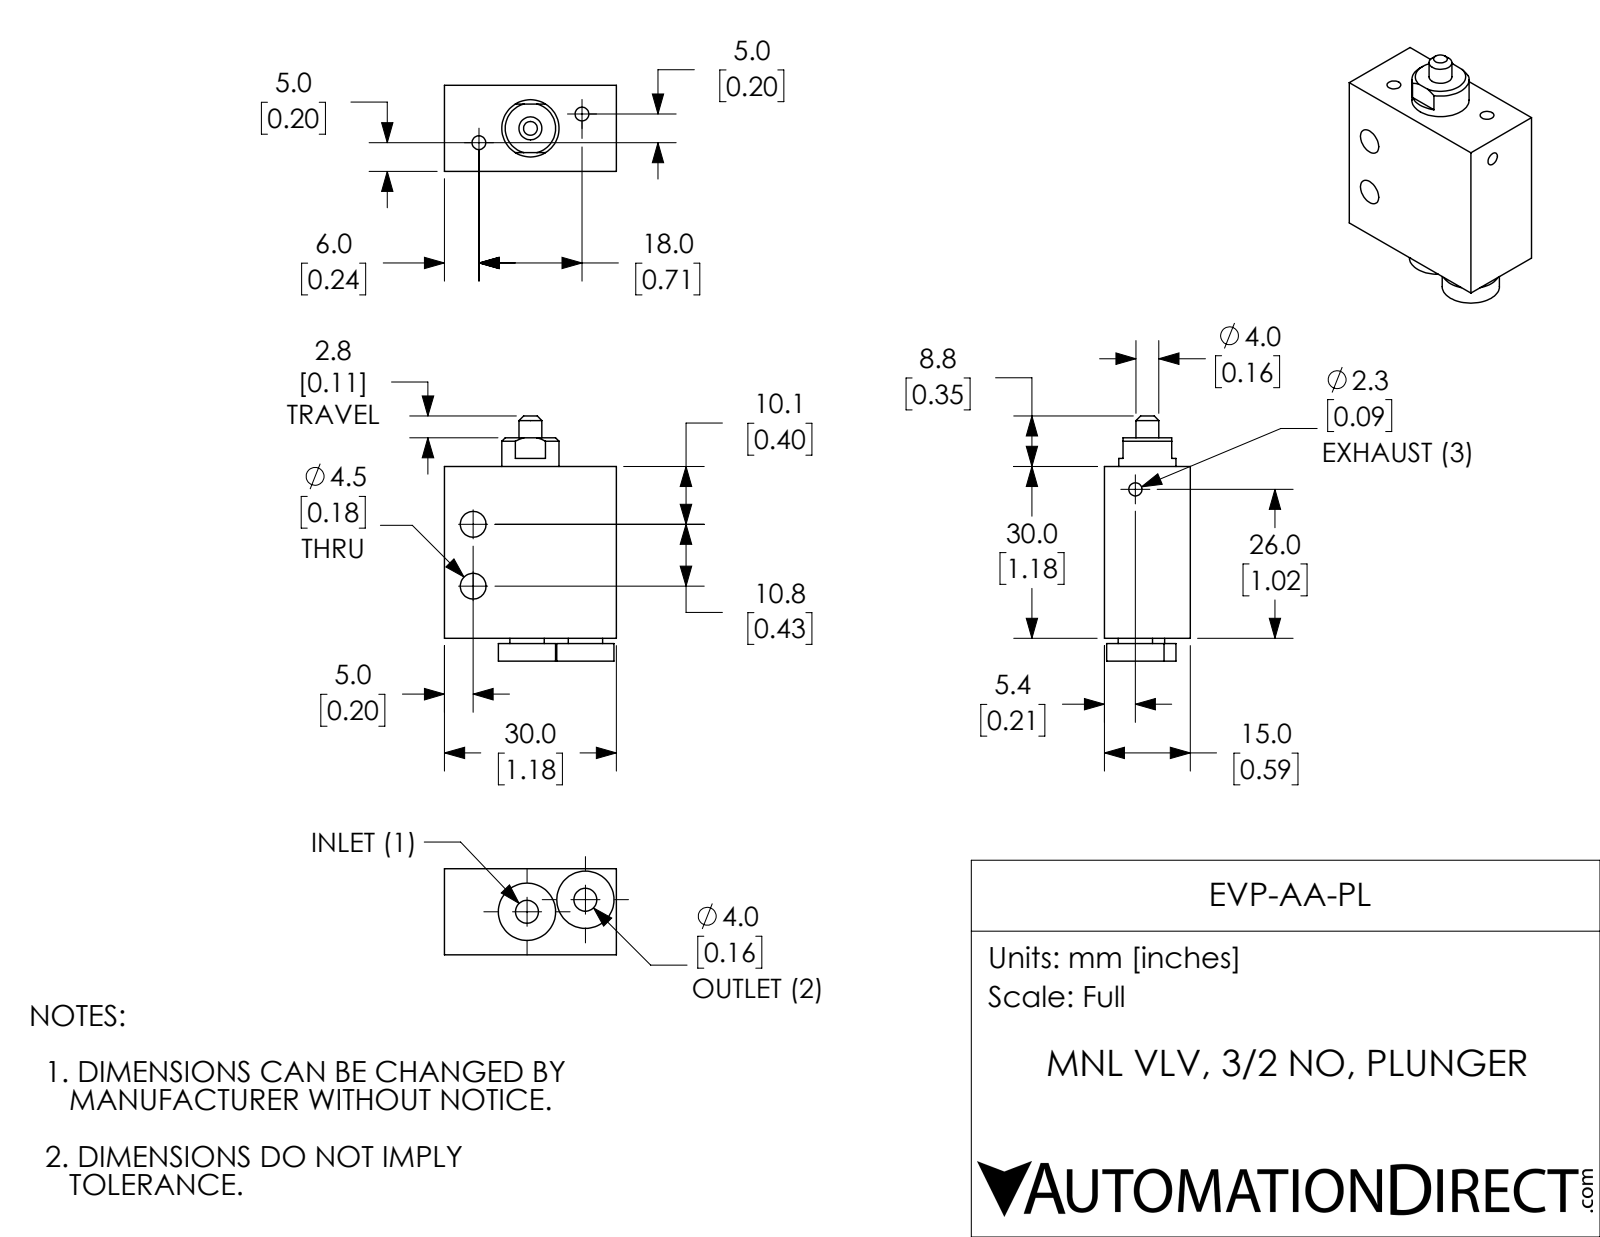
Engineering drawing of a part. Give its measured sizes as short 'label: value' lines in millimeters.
name: EVP-AA-PL
written by: SolidWorks 2017 (AUTOMOTIVE_DESIGN)
unit: mm
bodies: 1 solid, 51 faces (21 planar, 26 cylindrical, 4 other)
size: 42.8 × 30 × 15
volume: 13 800 mm³; area: 4 811 mm²
holes: 2× ⌀2.4, 2× ⌀4, 2× ⌀4.5, 1× ⌀2.3
bosses: 3× ⌀10, 2× ⌀6, 1× ⌀4
face distances: 15, 30, 4, 34, 3.1, 0.9, 30.9, 39, 35.9, 35
hole spacings: 4.6, 8.8, 9.9, 10.4, 10.8, 18.6, 18.7
